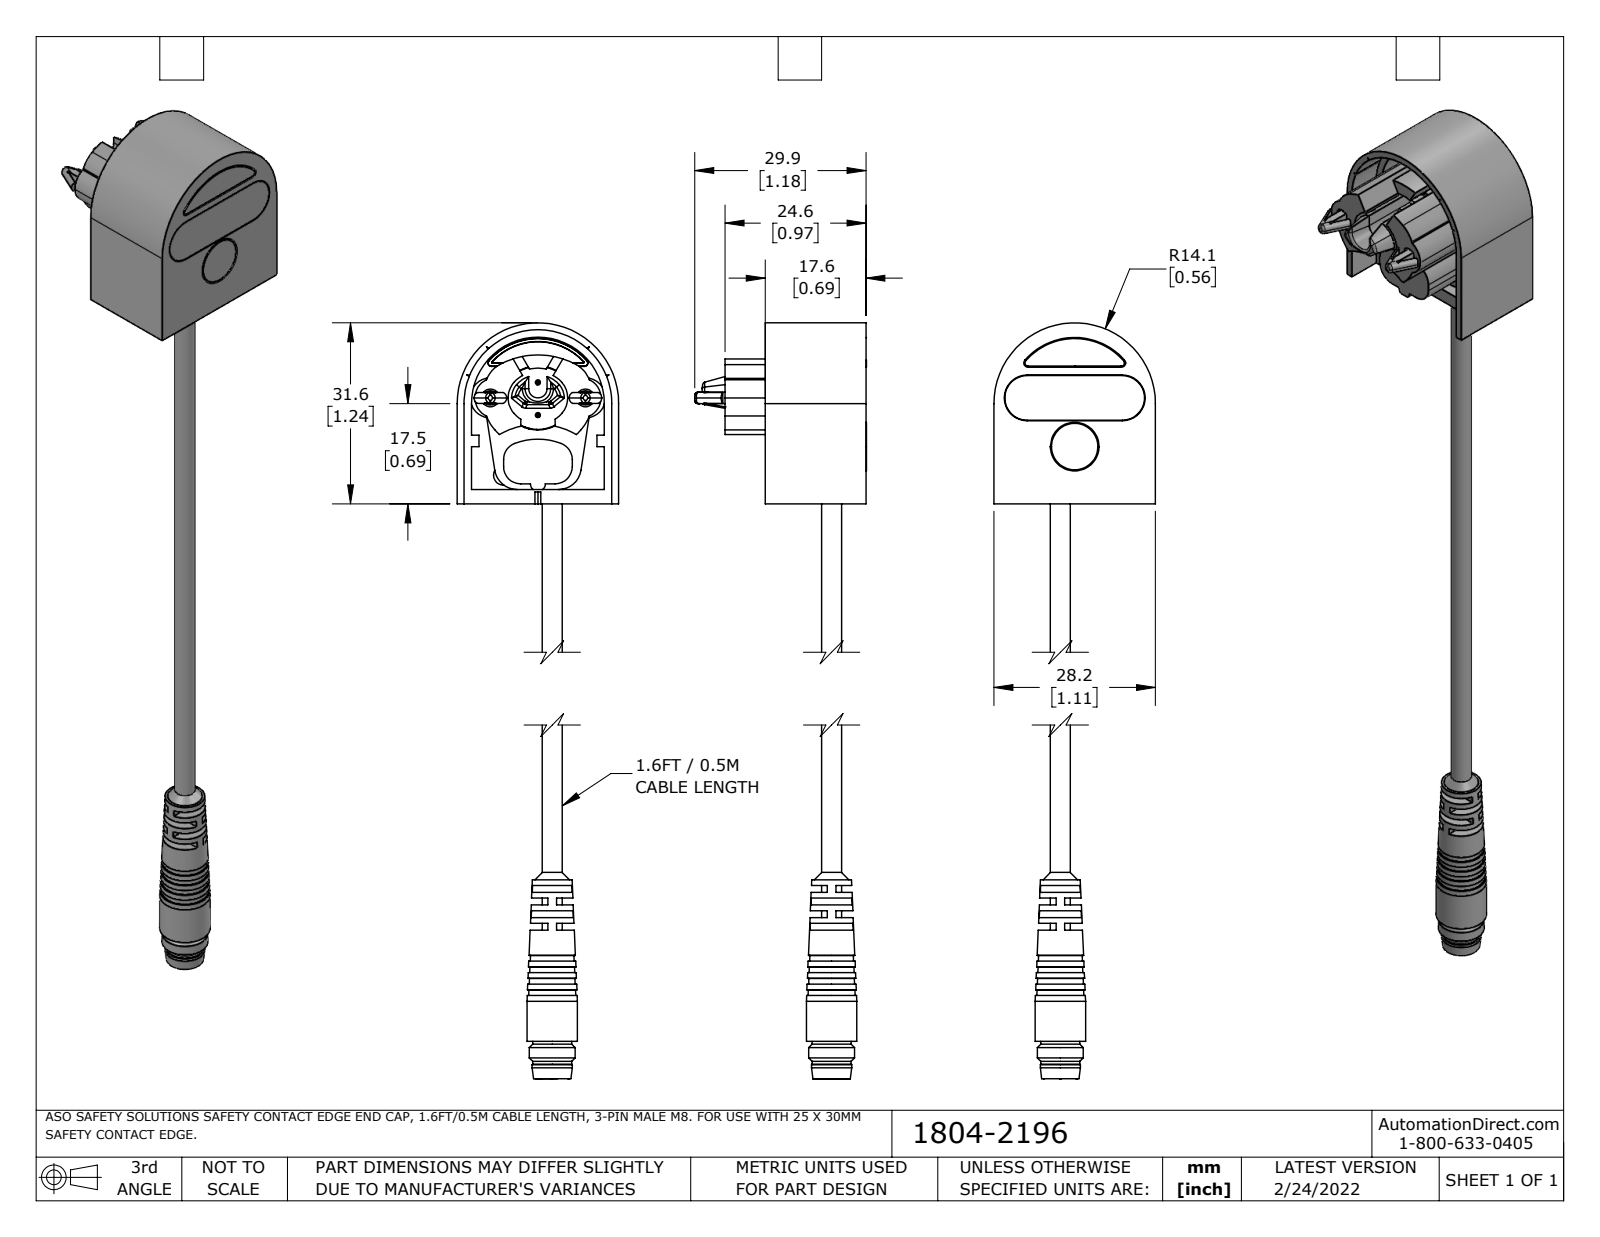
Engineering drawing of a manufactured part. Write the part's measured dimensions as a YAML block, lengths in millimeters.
part_name: "1804-2196_Default"
step_written_by: "SolidWorks 2021 (CONFIG_CONTROL_DESIGN)"
units: millimeters
bodies: {solids: 15, faces: 694, planar: 232, cylindrical: 284, other: 178}
overall_size: [172.4, 30, 28.2]
volume: 12601
surface_area: 13989
round_holes:
  - {diameter: 0.5, count: 4}
  - {diameter: 0.8, count: 3}
  - {diameter: 3.5, count: 3}
  - {diameter: 3.1, count: 2}
  - {diameter: 4, count: 2}
  - {diameter: 5.5, count: 2}
  - {diameter: 3.4, count: 1}
  - {diameter: 5.8, count: 1}
round_bosses_or_shafts:
  - {diameter: 1.2, count: 13}
  - {diameter: 0.5, count: 6}
  - {diameter: 3.5, count: 3}
  - {diameter: 1, count: 3}
  - {diameter: 5, count: 2}
  - {diameter: 2.5, count: 2}
  - {diameter: 2, count: 2}
  - {diameter: 1.66, count: 2}
partial_cylinders:
  - {radius: 1, count: 12}
  - {radius: 0.1, count: 9}
  - {radius: 0.3, count: 6}
  - {radius: 3, count: 6}
  - {radius: 3.5, count: 6}
  - {radius: 0.5, count: 5}
  - {radius: 4, count: 4}
  - {radius: 5, count: 4}
face_to_face_distances: [2.5, 1.8, 1, 1.2, 28.2, 0.8, 1.3, 2, 17.6, 7.8]
hole_center_spacings: [1.4, 16.6, 8.73, 8.83, 22.14, 22.66, 23.46, 23.95]
